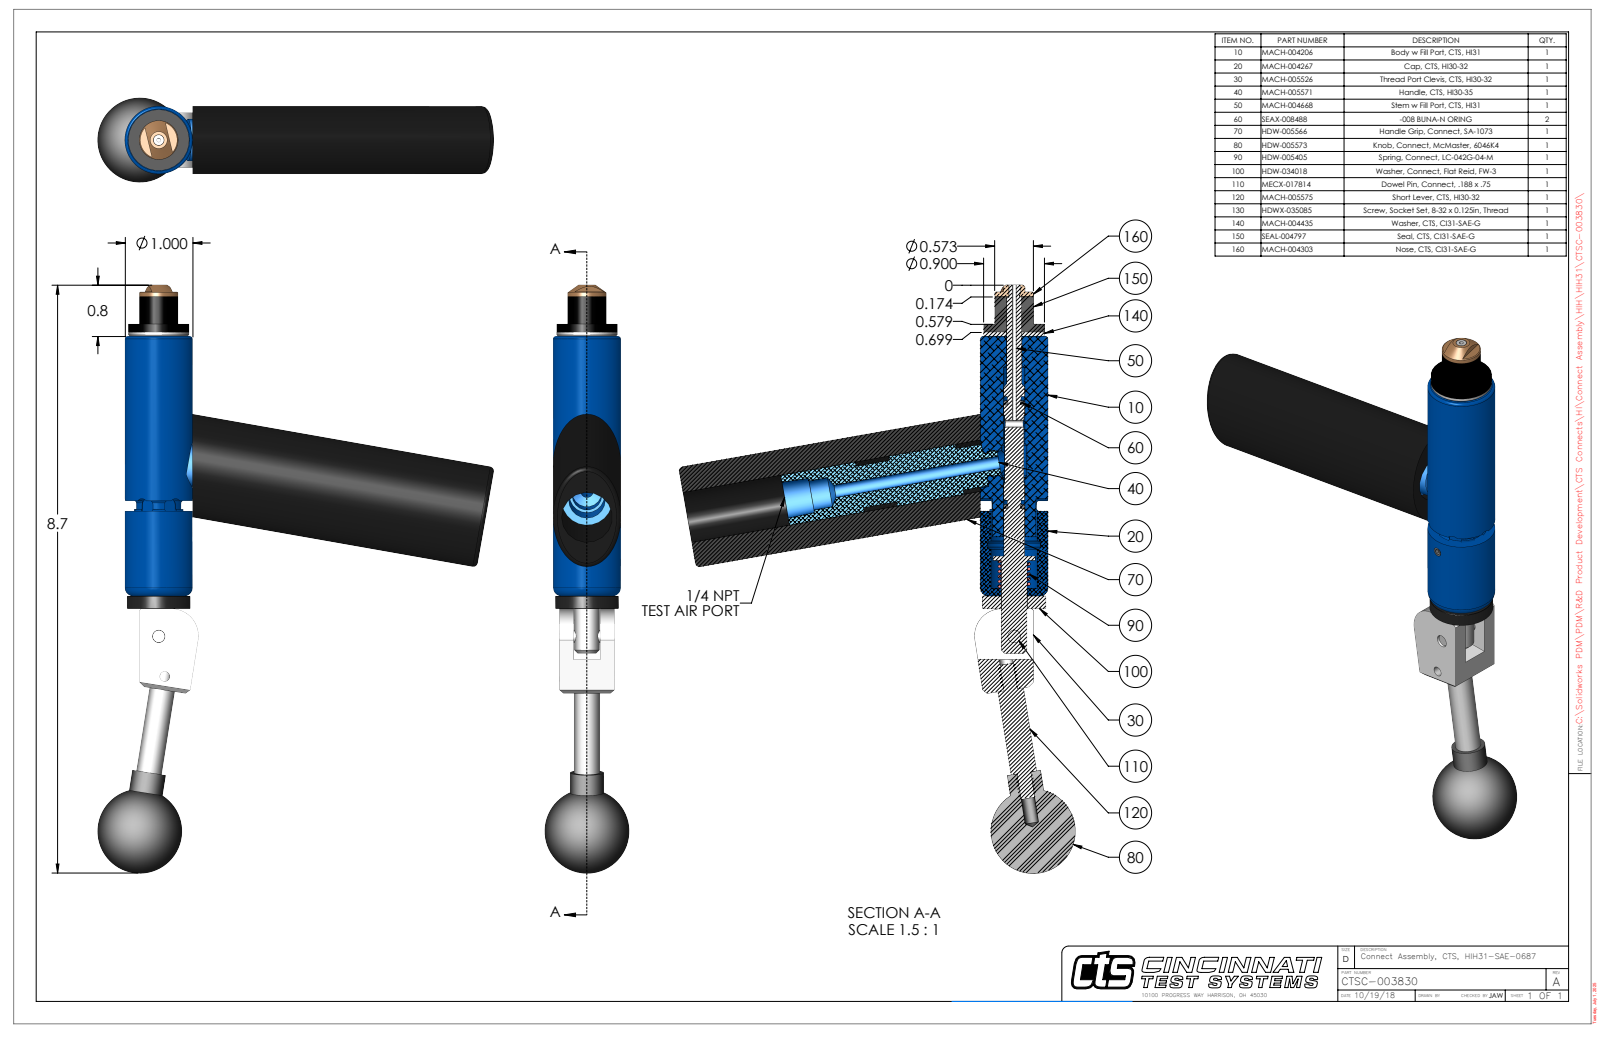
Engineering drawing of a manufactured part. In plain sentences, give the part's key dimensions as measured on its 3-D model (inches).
The part is named "CTSC-003830". Its 3-D file was written by "SolidWorks 2023 (AUTOMOTIVE_DESIGN)". It is 10 solids with 320 faces: 123 planar, 126 cylindrical and 71 other. Overall it measures 8.692 by 5.856 by 1.25 inches. Its volume is 9.389 cubic inches and its surface area 77.14 square inches. Round holes: 2 of diameter 0.201, 1 of diameter 0.063, 1 of diameter 0.109, 1 of diameter 0.136, 1 of diameter 0.15, 1 of diameter 0.159, 1 of diameter 0.187, 1 of diameter 0.189, 1 of diameter 0.218, 1 of diameter 0.228, 1 of diameter 0.229, 1 of diameter 0.385. Round bosses or shafts: 1 of diameter 1, 1 of diameter 0.936, 1 of diameter 0.9, 1 of diameter 0.75, 1 of diameter 0.62, 1 of diameter 0.573, 1 of diameter 0.5, 1 of diameter 0.38. Partial cylindrical surfaces (rounded edges, fillets, slot ends): 6 of radius 0.093, 2 of radius 0.029, 1 of radius 0.064, 1 of radius 0.325, 1 of radius 0.375, 1 of radius 0.4, 1 of radius 0.445. The main face-to-face distances are 0.21, 0.602, 0.06, 3.896, 3.835, 0.812, 4.083, 4.023, 0.187, 0.391. The hole center spacings are 0.599, 1.658, 2.252.
